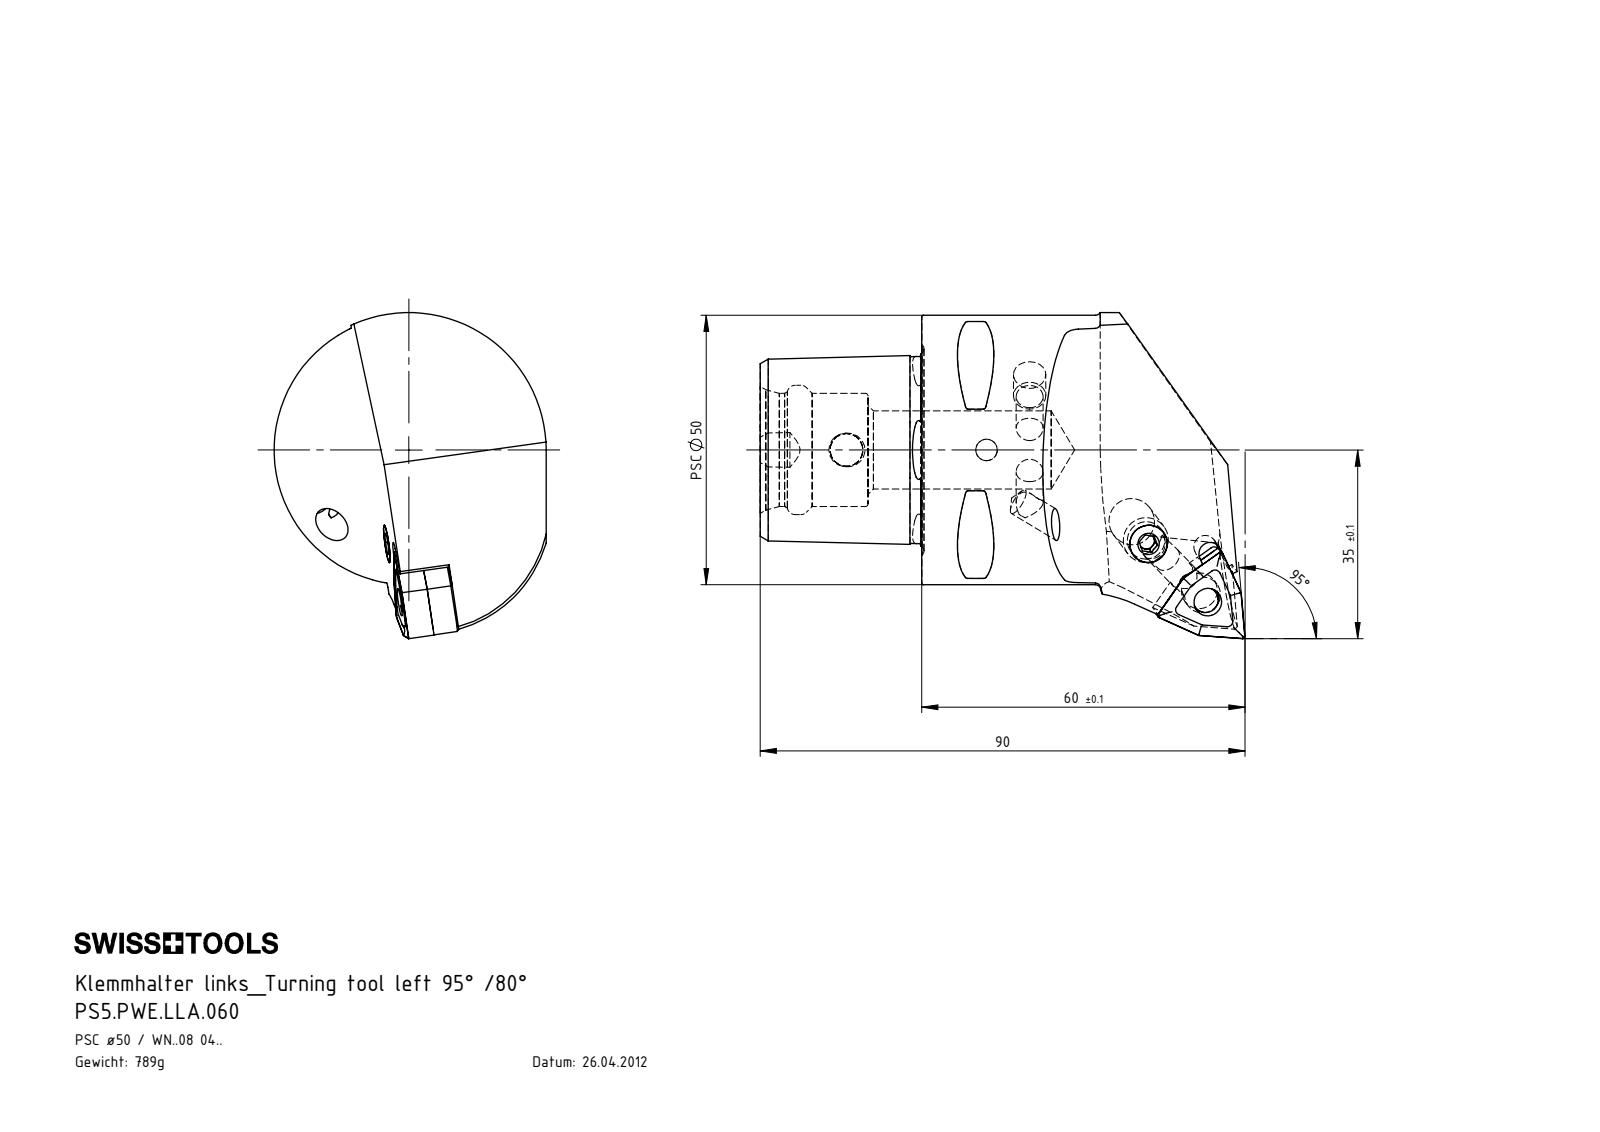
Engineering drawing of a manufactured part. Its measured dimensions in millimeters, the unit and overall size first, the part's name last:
Units: millimetres
Overall size (bounding box): 90 × 60.5 × 50.5
Round holes (diameter × count): ⌀5 ×3, ⌀4 ×1, ⌀5.16 ×1, ⌀6 ×1, ⌀6.1 ×1, ⌀6.4 ×1, ⌀6.7 ×1, ⌀7 ×1, ⌀7.8 ×1, ⌀8.4 ×1, ⌀14.5 ×1, ⌀21 ×1
Round bosses / shafts (diameter × count): ⌀50 ×1, ⌀8 ×1, ⌀7.9 ×1, ⌀6.4 ×1, ⌀6 ×1, ⌀4.7 ×1, ⌀3.55 ×1
Partial cylindrical surfaces — rounded edges, fillets, slot ends (radius × count): R0.5 ×8, R0.4 ×3, R1 ×3, R2.5 ×3, R2.1 ×1, R2.3 ×1, R2.35 ×1, R2.8 ×1
Main face-to-face distances: 30, 4.76, 4.46, 9.22, 19.18, 44.4, 5, 20, 10, 6.3
Hole centre spacings: 15.6, 15.61, 26
Volume: 99 892 mm³ · Surface area: 22 671 mm²
Bodies: 8 solids, 360 faces (101 planar, 86 cylindrical, 173 other)
Part name (STEP PRODUCT): WWE-ER2.101.004_A; PS5.PWE.LLA.060; WCD-ER4.101.017_A; KVT_MB_600_060 (+4 more)
STEP written by: SolidWorks 2017 (AUTOMOTIVE_DESIGN)
